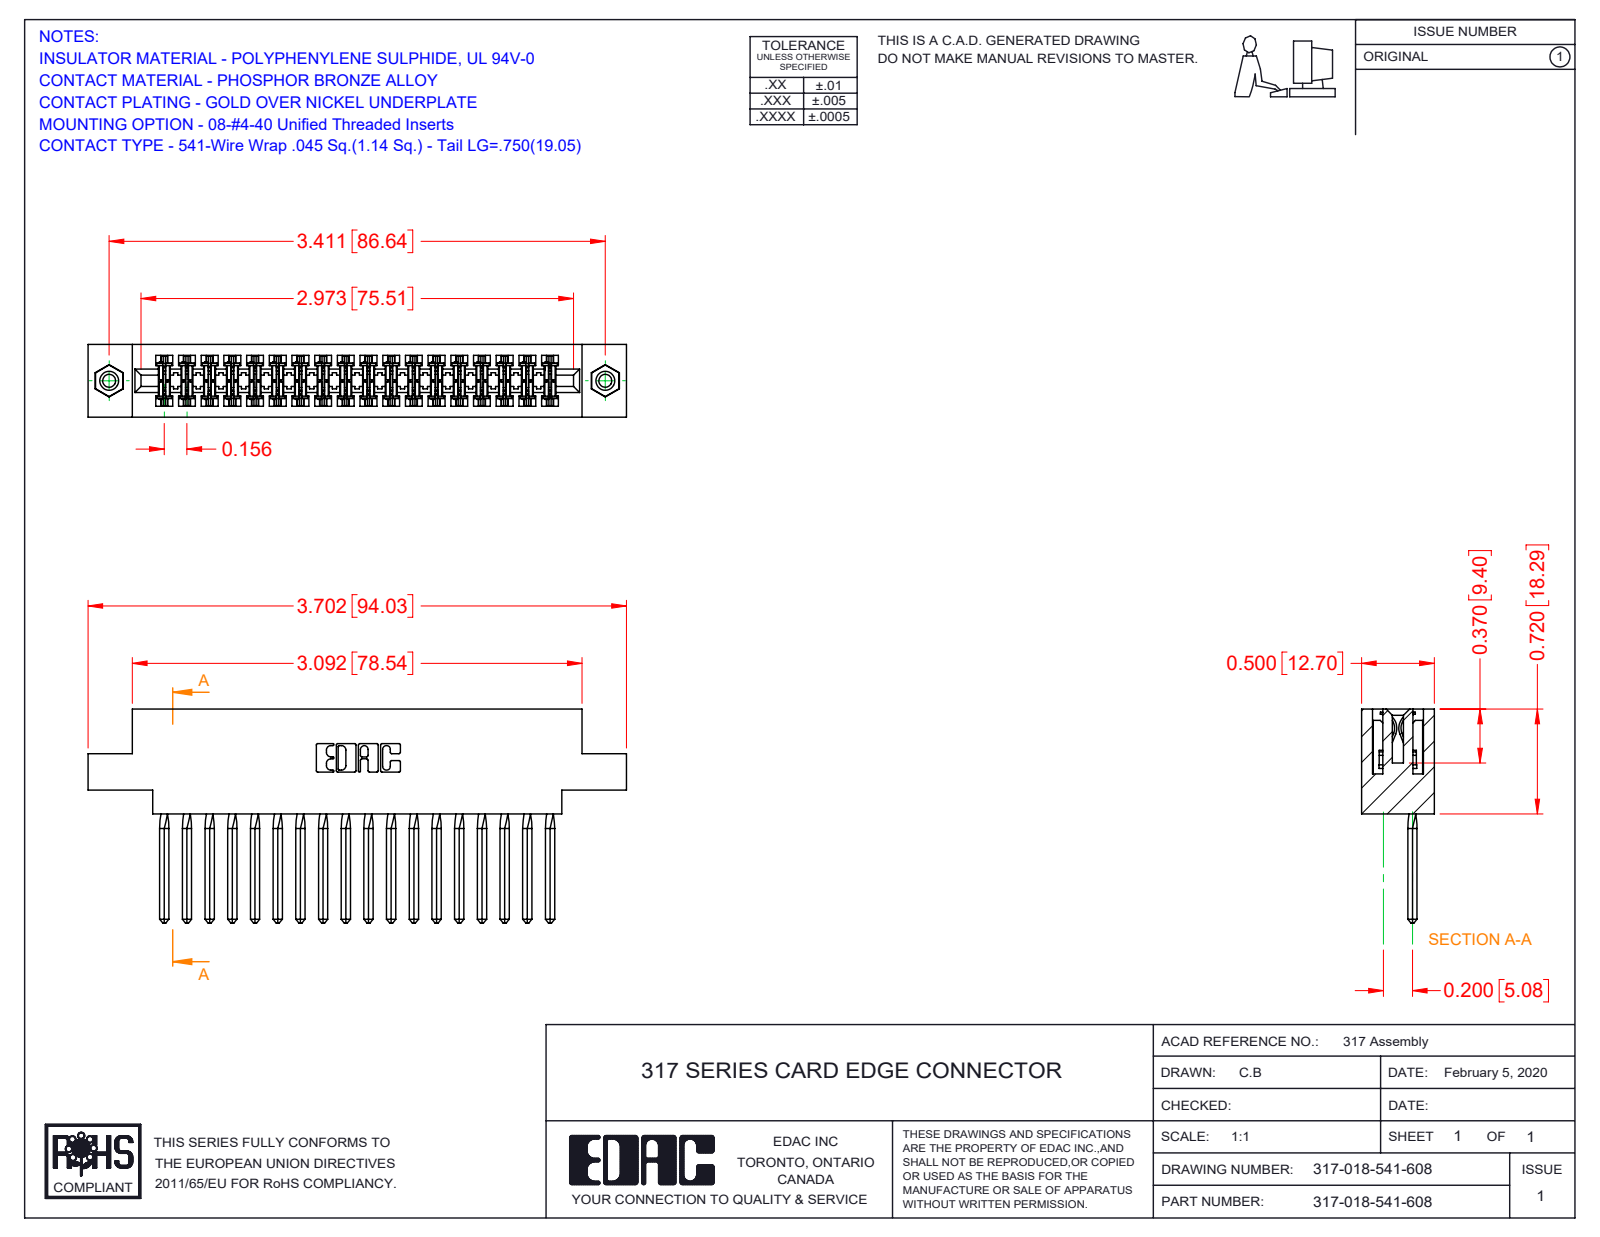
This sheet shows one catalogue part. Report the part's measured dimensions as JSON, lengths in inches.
{"part_name": "317-018-541-678; 345-250-001_345-250-003-102; 317-290-002_541; 317 Part_.156 Dia - TI", "step_written_by": "SolidWorks 2016 (CONFIG_CONTROL_DESIGN)", "units": "inches", "bodies": {"solids": 21, "faces": 2898, "planar": 2322, "cylindrical": 488, "other": 88}, "overall_size": [3.702, 1.47, 0.5], "volume_in3": 0.885, "surface_area_in2": 30.56, "round_holes": [[0.089, 2], [0.125, 2], [0.156, 2]], "round_bosses_or_shafts": [[0.155, 2]], "partial_cylinders_radius": [[0.015, 36], [0.01, 22], [0.007, 6], [0.031, 6], [0.026, 3], [0.095, 2], [0.1, 2], [0.11, 2]], "face_to_face_distances": [0.5, 0.075, 0.425, 0.11, 0.35, 0.195, 0.22, 0.772, 0.72, 0.662], "hole_center_spacings": [3.411]}
